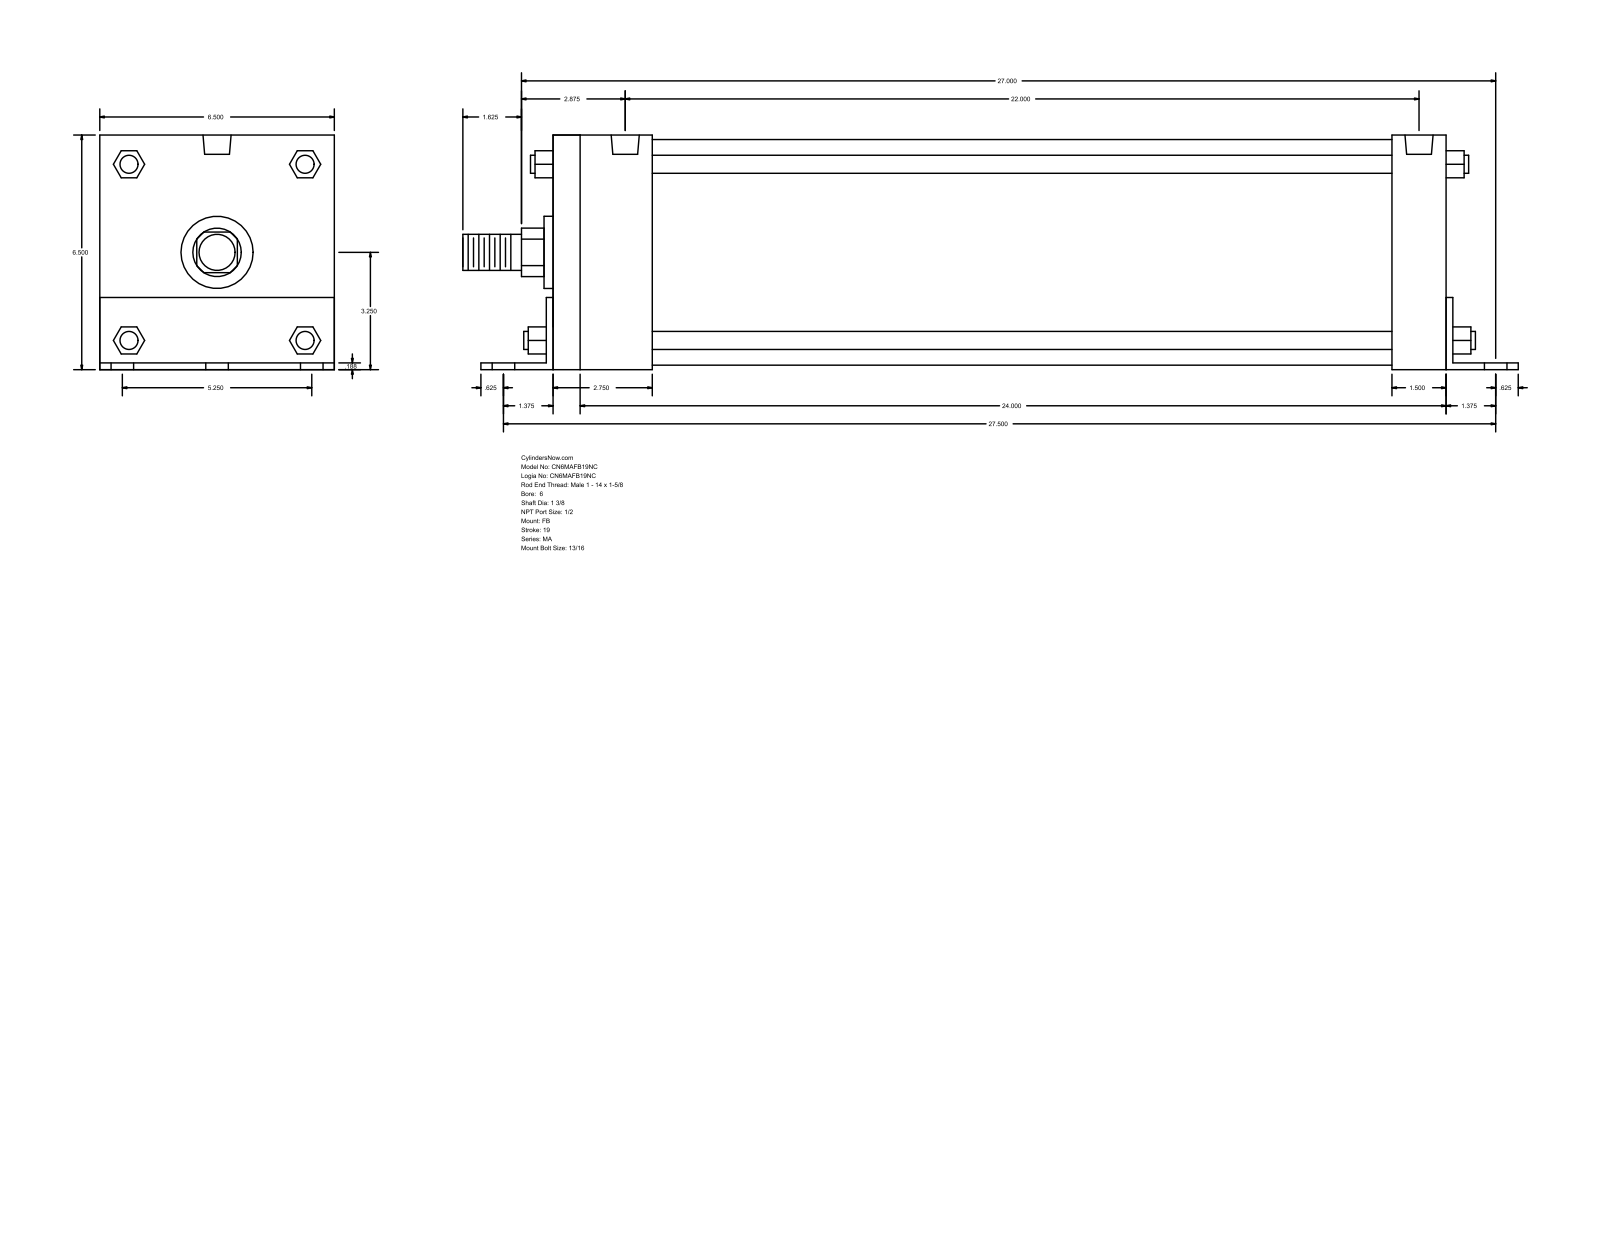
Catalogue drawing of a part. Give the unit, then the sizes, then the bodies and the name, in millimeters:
Units: millimetres
Overall size (bounding box): 739.77 × 165.15 × 165.1
Round holes (diameter × count): ⌀20.64 ×6, ⌀17.46 ×4, ⌀19.77 ×2
Round bosses / shafts (diameter × count): ⌀12.7 ×4, ⌀158.75 ×1, ⌀50.8 ×1, ⌀34.92 ×1, ⌀25.4 ×1
Partial cylindrical surfaces — rounded edges, fillets, slot ends (radius × count): R17.06 ×1, R32.05 ×1
Main face-to-face distances: 165.1, 4.76, 625.47, 165.15, 4.71, 160.39, 4.77, 38.1, 42.86, 635
Hole centre spacings: 66.67, 698.51, 695.32, 83.81, 85.78, 108.6, 133.34, 555.62
Bodies: 0 solids, 140 faces (105 planar, 35 cylindrical, 0 other)
Part name (STEP PRODUCT): MA_FB__0600_1.375
STEP written by: GSSL Pune (CONFIG_CONTROL_DESIGN)
